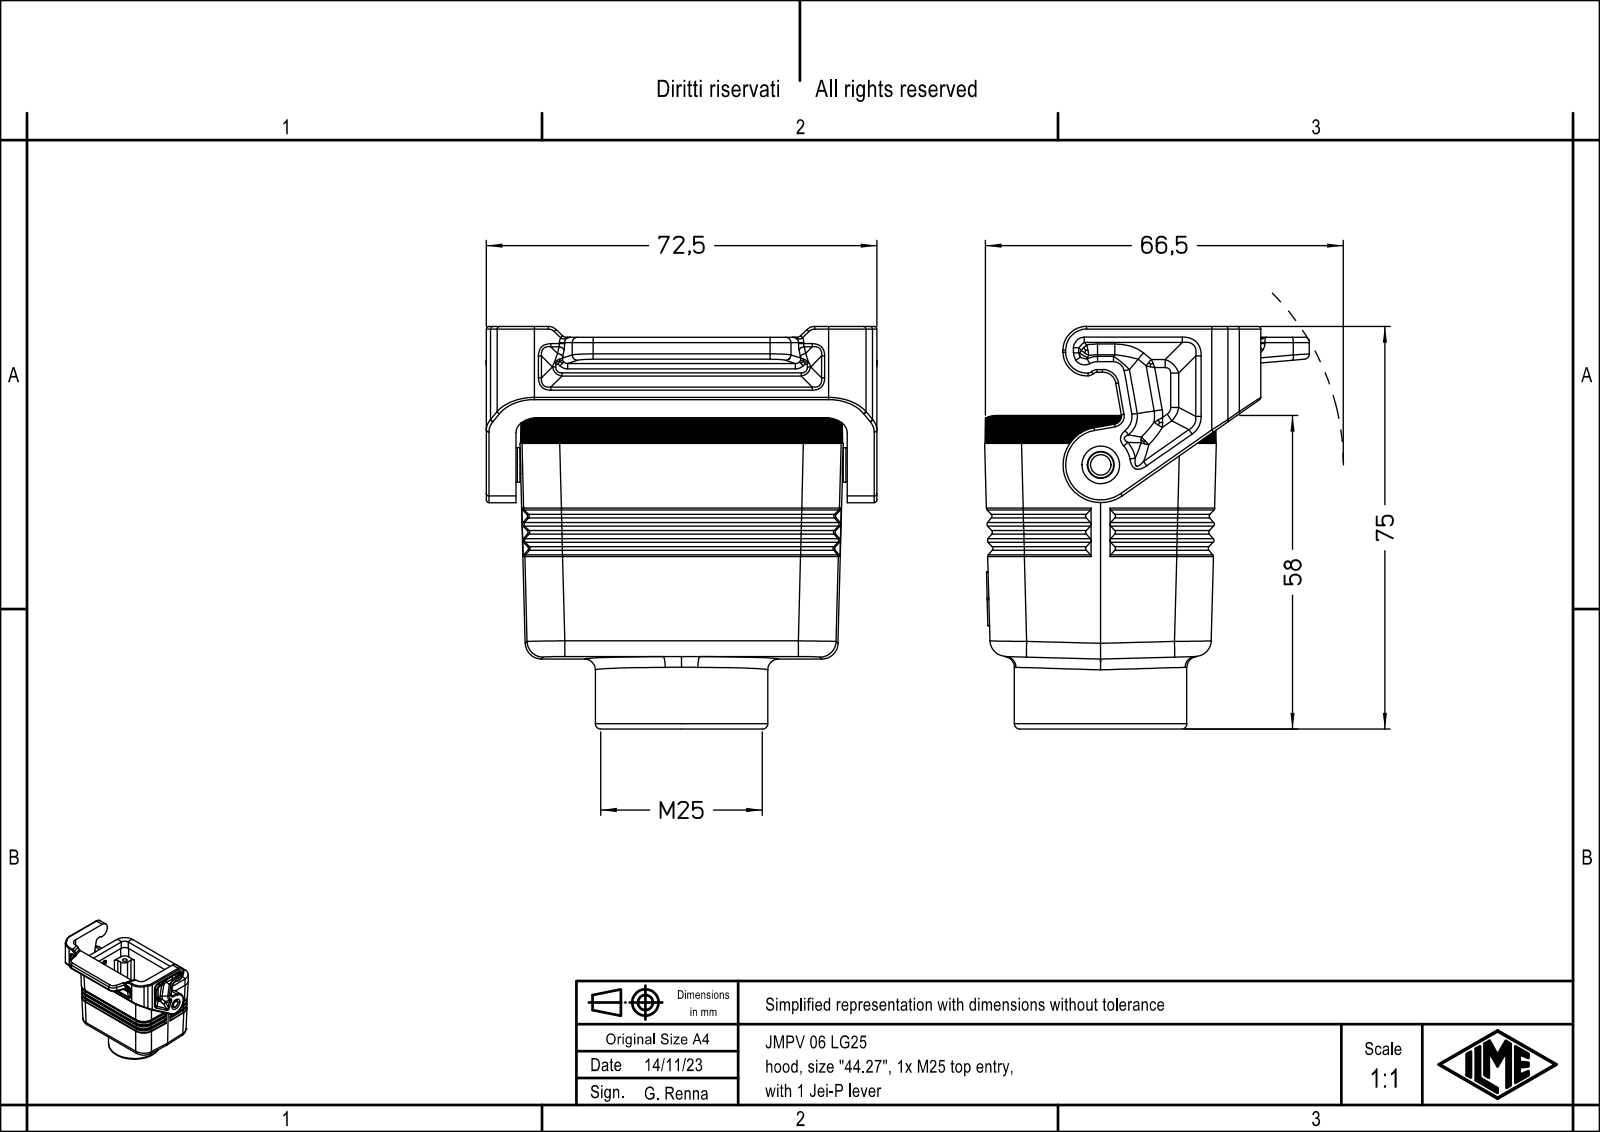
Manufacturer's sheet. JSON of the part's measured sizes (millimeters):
{"part_name": "JMPV 06 LG25", "step_written_by": "Creo Elements/Direct Modeling 20.1B 02-Apr-2019 (C) Parametric Technology GmbH (AUTOMOTIVE_DESIGN)", "units": "millimeters", "bodies": {"solids": 1, "faces": 706, "planar": 217, "cylindrical": 191, "other": 298}, "overall_size": [74.7, 72.58, 60.25], "volume_mm3": 54073, "surface_area_mm2": 29864, "round_holes": [[18, 1], [23.6, 1]], "round_bosses_or_shafts": [[32, 1], [6.4, 1], [4.8, 1]], "partial_cylinders_radius": [[0.5, 36], [3, 22], [1, 19], [1.5, 18], [0.33, 15], [2, 12], [7, 9], [4, 8]], "face_to_face_distances": [2, 61.5, 56.9, 5.5, 67, 0.41, 39.31, 38.9, 7, 58.9]}
